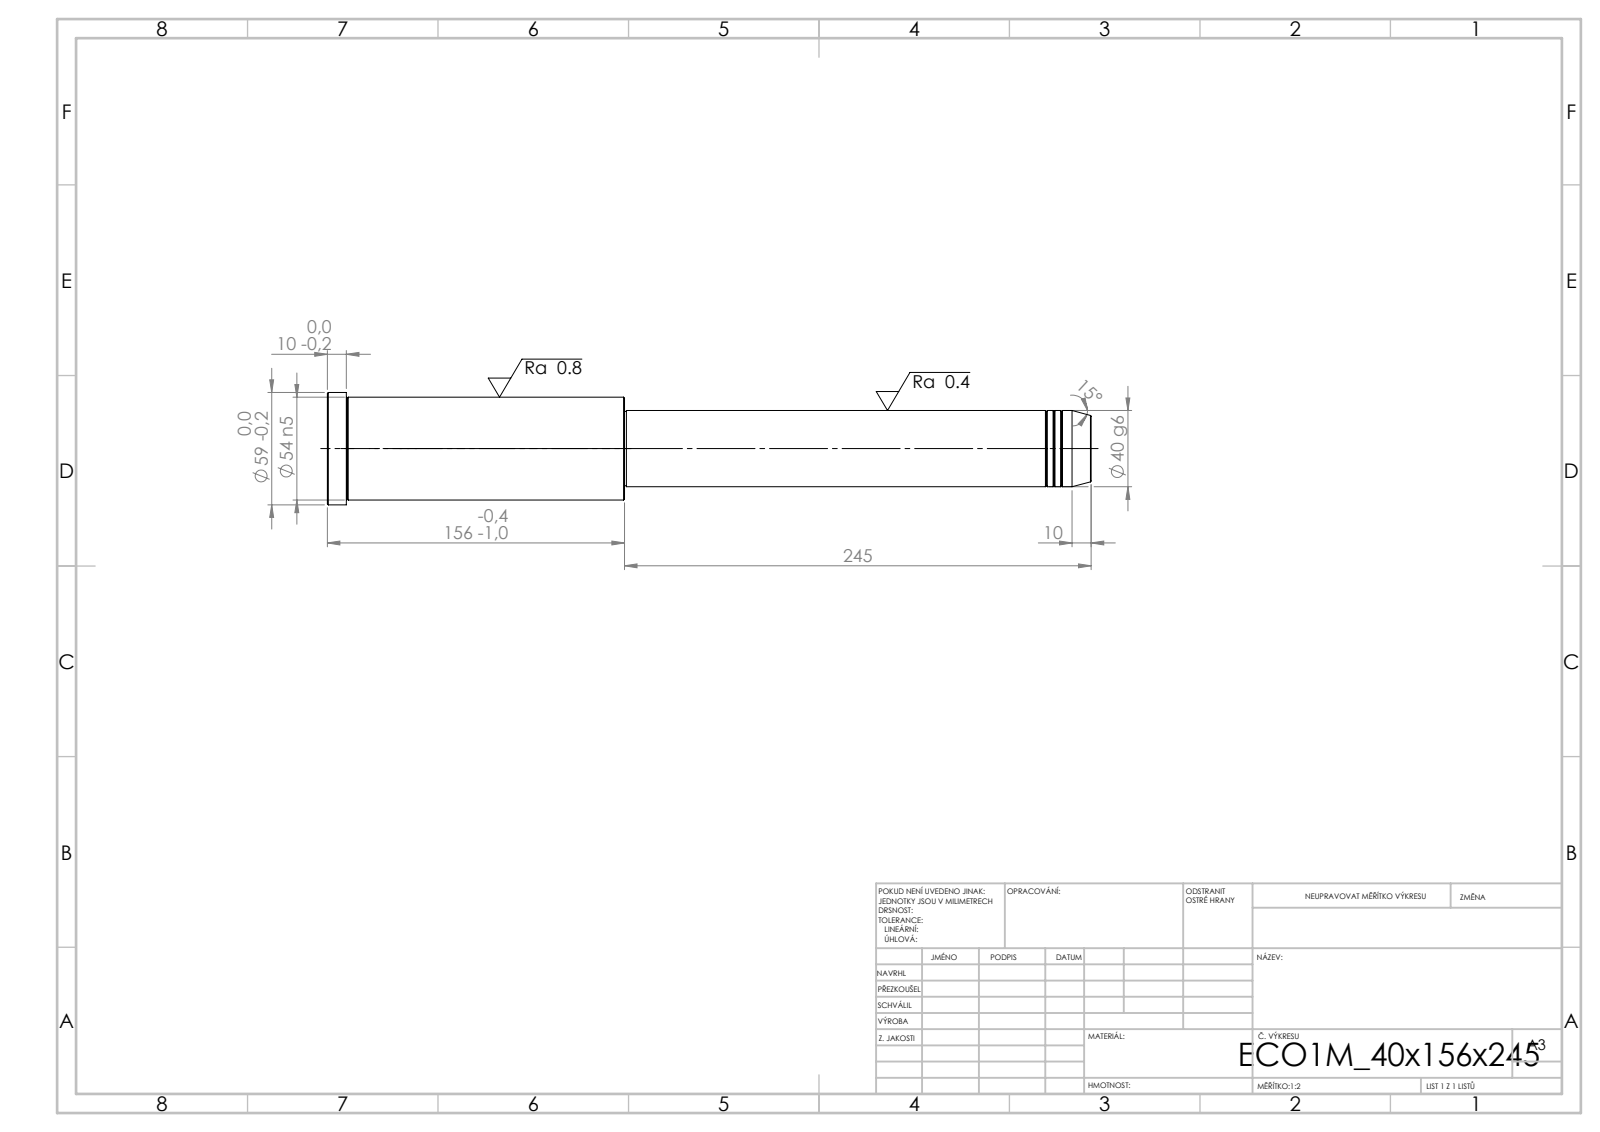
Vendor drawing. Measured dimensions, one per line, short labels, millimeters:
written by: SolidWorks 2019 (CONFIG_CONTROL_DESIGN)
unit: mm
bodies: 1 solid, 43 faces (5 planar, 14 cylindrical, 24 other)
size: 401 × 59 × 59
volume: 667 658 mm³; area: 62 824 mm²
bosses: 1× ⌀59, 1× ⌀54, 1× ⌀40, 1× ⌀39
face distances: 156, 245, 401, 391, 146, 10, 244, 1, 147, 157
